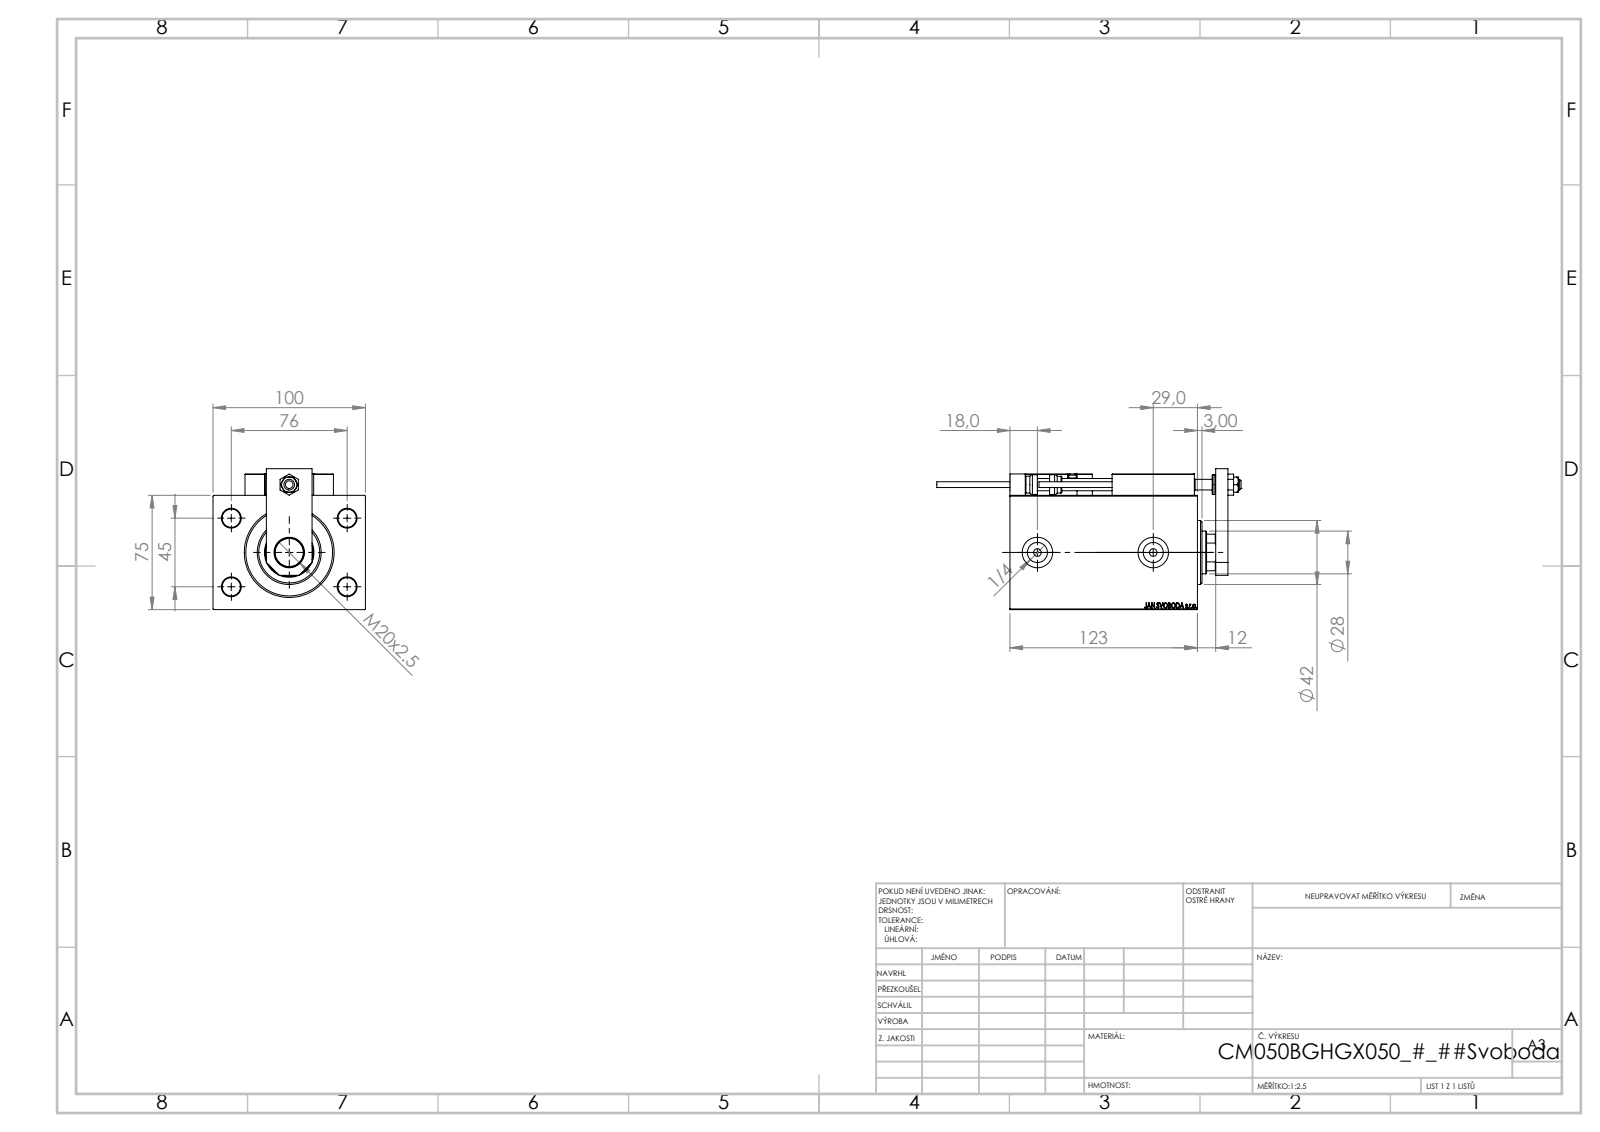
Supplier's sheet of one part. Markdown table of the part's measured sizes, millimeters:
| quantity | value |
| --- | --- |
| part name | V450CM_B_VCP; ZARAZKA; SWITCH DIM B,W; TYC_L79 (+8 more) |
| STEP written by | SolidWorks 2019 (CONFIG_CONTROL_DESIGN) |
| units | millimeters |
| bodies | 24 solids, 1321 faces (562 planar, 186 cylindrical, 573 other) |
| overall size | 199.7 × 100 × 92.5 |
| volume | 890 122 mm³ |
| surface area | 137 111 mm² |
| round holes (diameter × count) | 8 × 5, 3.2 × 4, 4 × 4, 5 × 4, 12 × 4, 20 × 3, 13.16 × 2, 7 × 1, 18.5 × 1, 28 × 1, 31.5 × 1, 32.5 × 1 |
| round bosses / shafts (diameter × count) | 5 × 2, 3.8 × 2, 42 × 1, 13 × 1, 11 × 1 |
| partial cylindrical surfaces (radius × count) | 0.3 × 30, 3 × 2, 13.5 × 1 |
| main face-to-face distances | 75, 100, 14, 123, 12, 109, 24, 111, 20, 8 |
| hole center spacings | 44.16, 76, 11.37, 20, 29.59, 29.69, 36.06, 42.19 |
